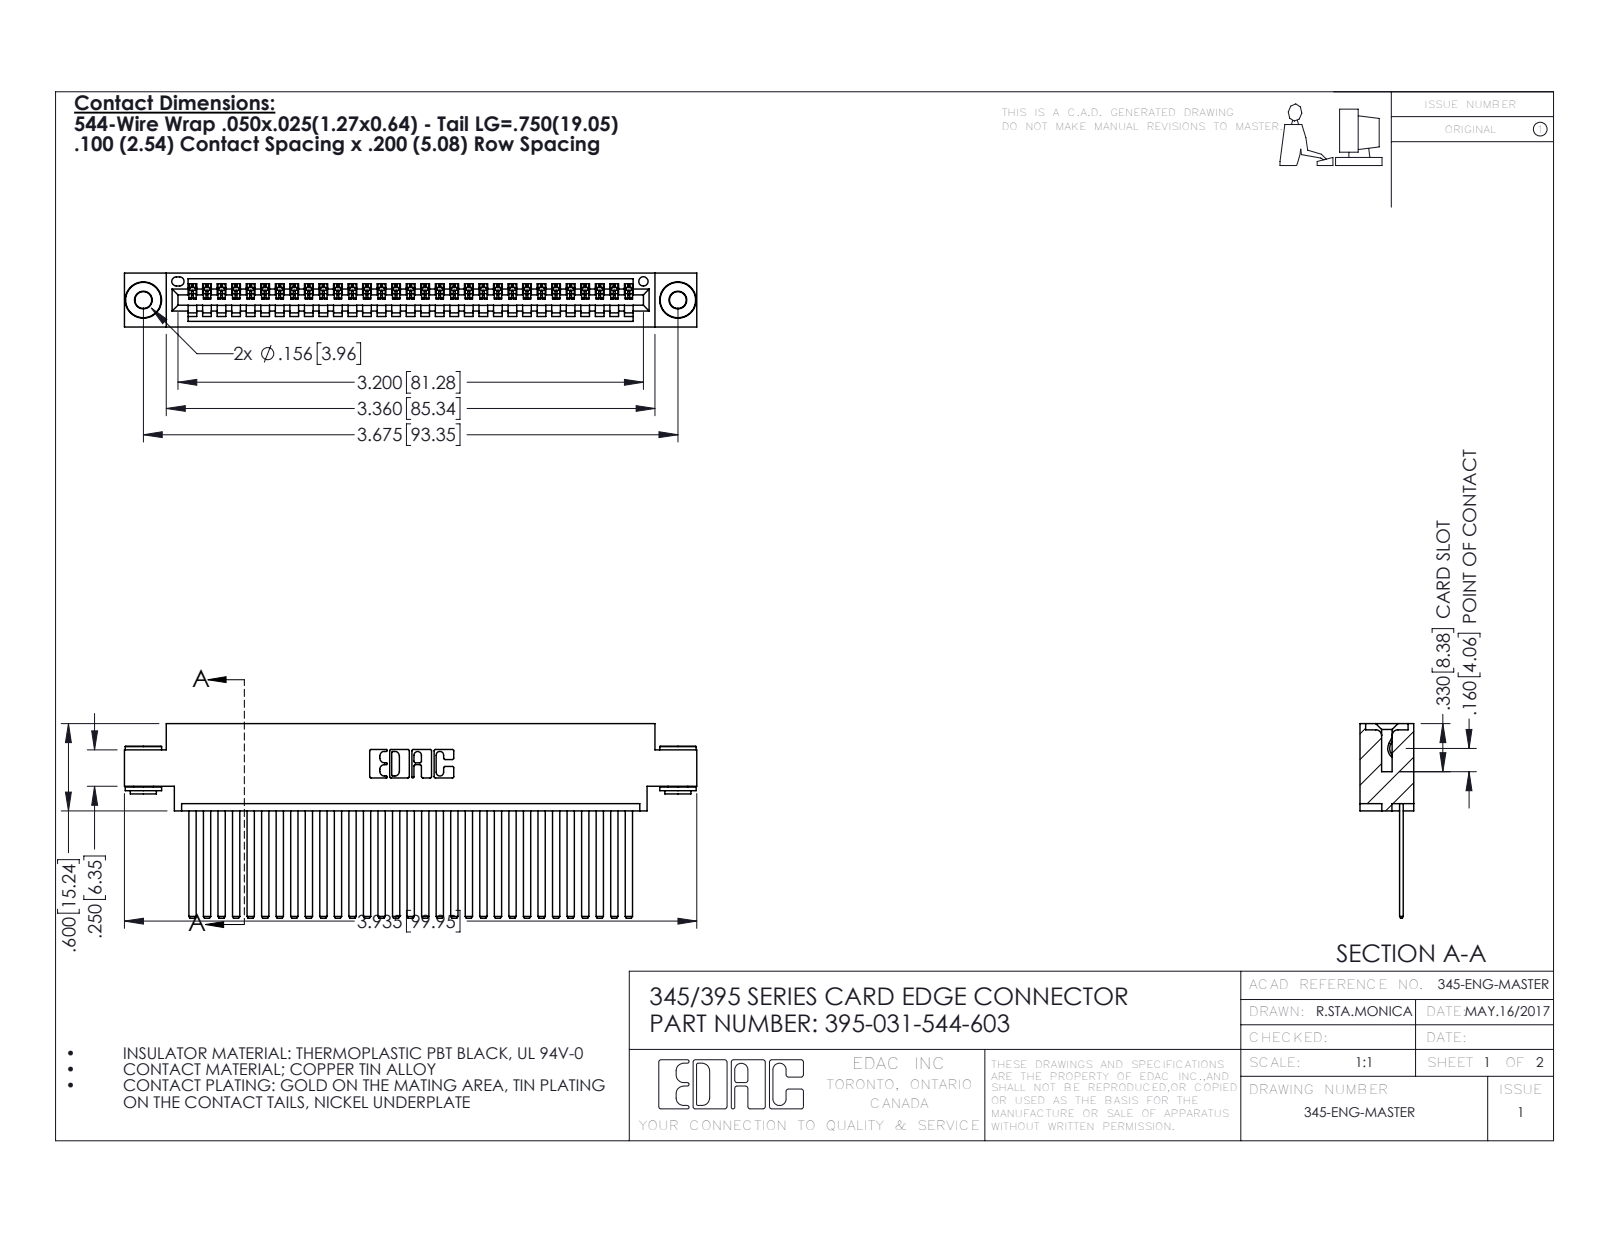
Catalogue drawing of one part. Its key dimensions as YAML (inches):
part_name: "395-031-544-603; 345-292-001_345-293-144; 345-250-002_345-250-002-102; 345 Part_0.170 Offset - 0.156 Dia-TH"
step_written_by: "SolidWorks 2016 (CONFIG_CONTROL_DESIGN)"
units: inches
bodies: {solids: 34, faces: 1780, planar: 1210, cylindrical: 562, other: 8}
overall_size: [3.935, 1.337, 0.37]
volume: 0.59
surface_area: 21.88
round_holes:
  - {diameter: 0.116, count: 2}
  - {diameter: 0.156, count: 2}
  - {diameter: 0.064, count: 1}
round_bosses_or_shafts:
  - {diameter: 0.25, count: 2}
  - {diameter: 0.18, count: 2}
  - {diameter: 0.136, count: 2}
partial_cylinders:
  - {radius: 0.006, count: 62}
  - {radius: 0.01, count: 22}
  - {radius: 0.007, count: 6}
  - {radius: 0.031, count: 6}
  - {radius: 0.026, count: 3}
  - {radius: 0.031, count: 2}
  - {radius: 0.04, count: 2}
  - {radius: 0.014, count: 1}
face_to_face_distances: [0.072, 0.298, 0.025, 0.098, 0.272, 0.37, 0.2, 0.225, 0.175, 0.149]
hole_center_spacings: [0.27, 3.44, 3.675]
